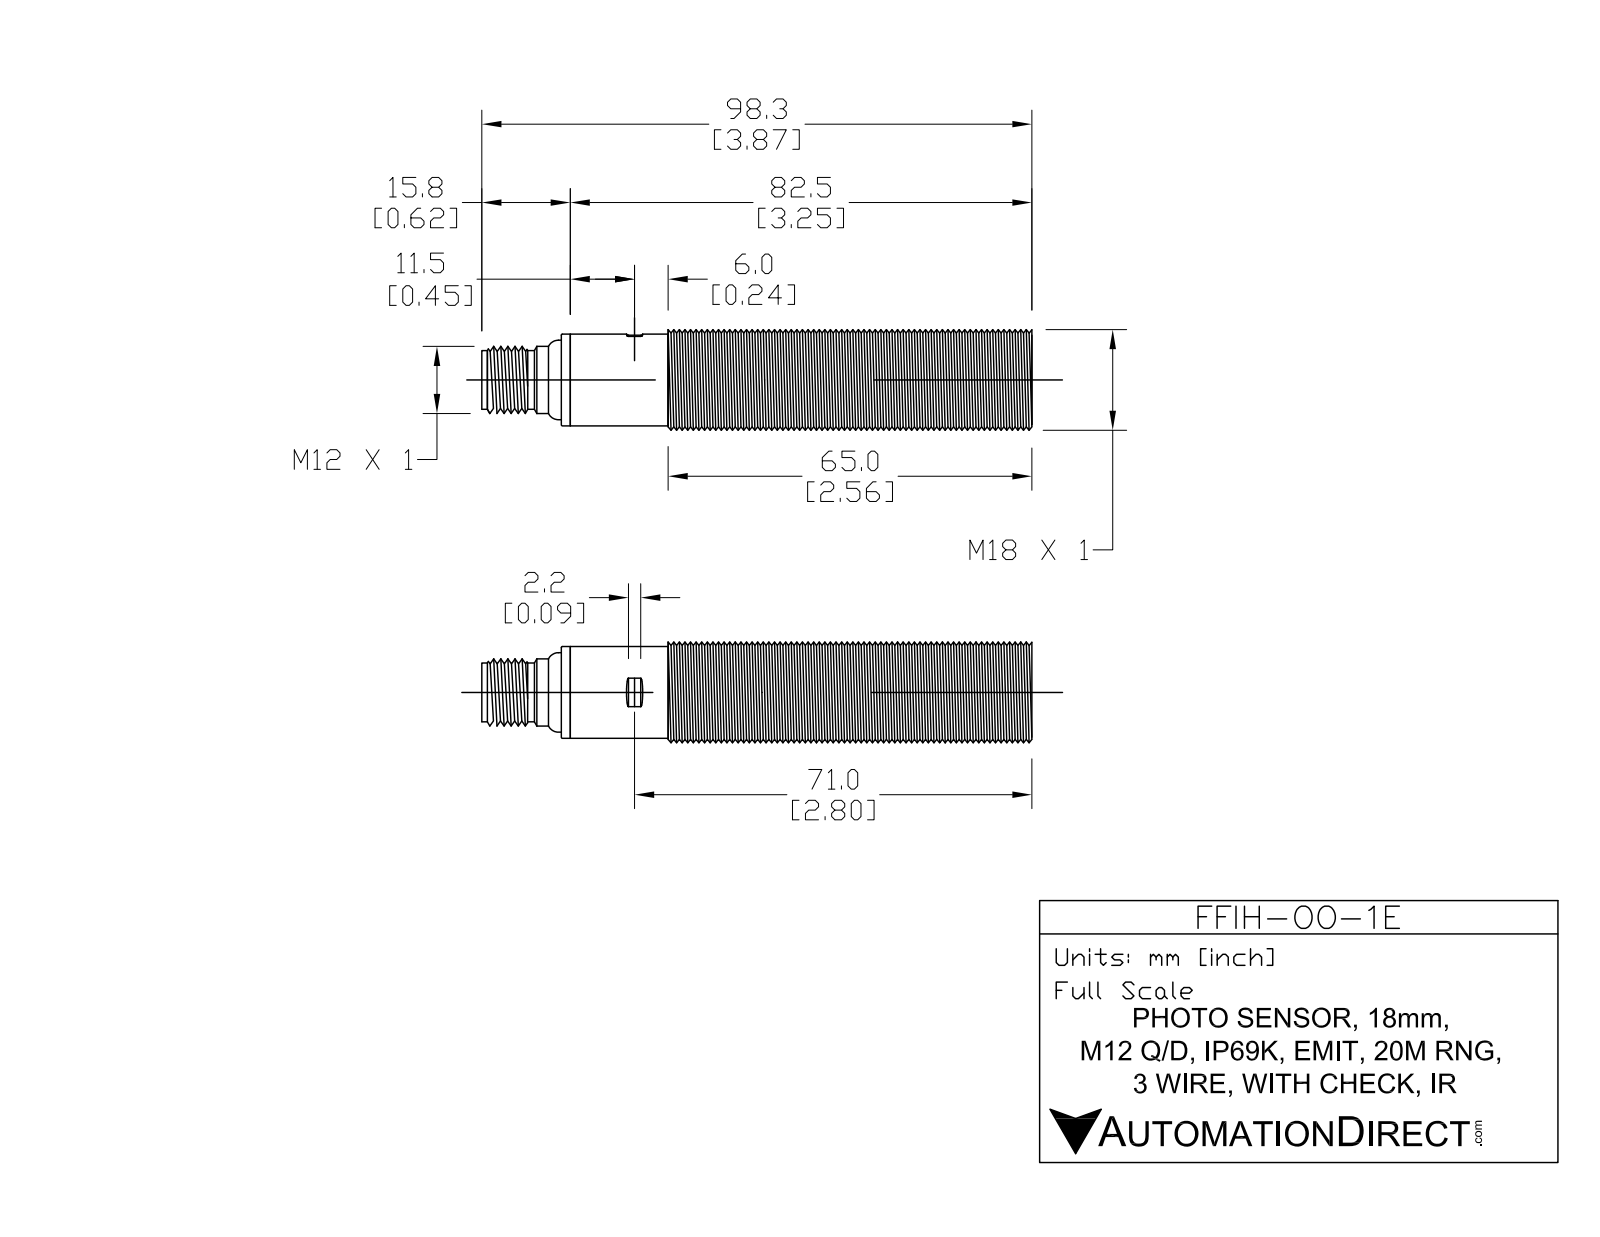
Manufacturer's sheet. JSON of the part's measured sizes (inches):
{"part_name": "FFIH-00-1E", "step_written_by": "SolidWorks 2017 (AUTOMOTIVE_DESIGN)", "units": "inches", "bodies": {"solids": 5, "faces": 118, "planar": 21, "cylindrical": 48, "other": 49}, "overall_size": [3.268, 0.709, 0.709], "volume_in3": 1.081, "surface_area_in2": 10.47, "round_holes": [[0.278, 1], [0.327, 1], [0.5, 1], [0.583, 1], [0.61, 1]], "round_bosses_or_shafts": [[0.039, 4], [0.709, 1], [0.646, 1], [0.612, 1], [0.604, 1], [0.559, 1], [0.492, 1], [0.472, 1]], "partial_cylinders_radius": [[0.024, 1], [0.63, 1]], "face_to_face_distances": [2.539, 0.118, 2.657, 0.024, 0.094, 2.634, 2.717, 2.693, 2.598, 0.059]}
